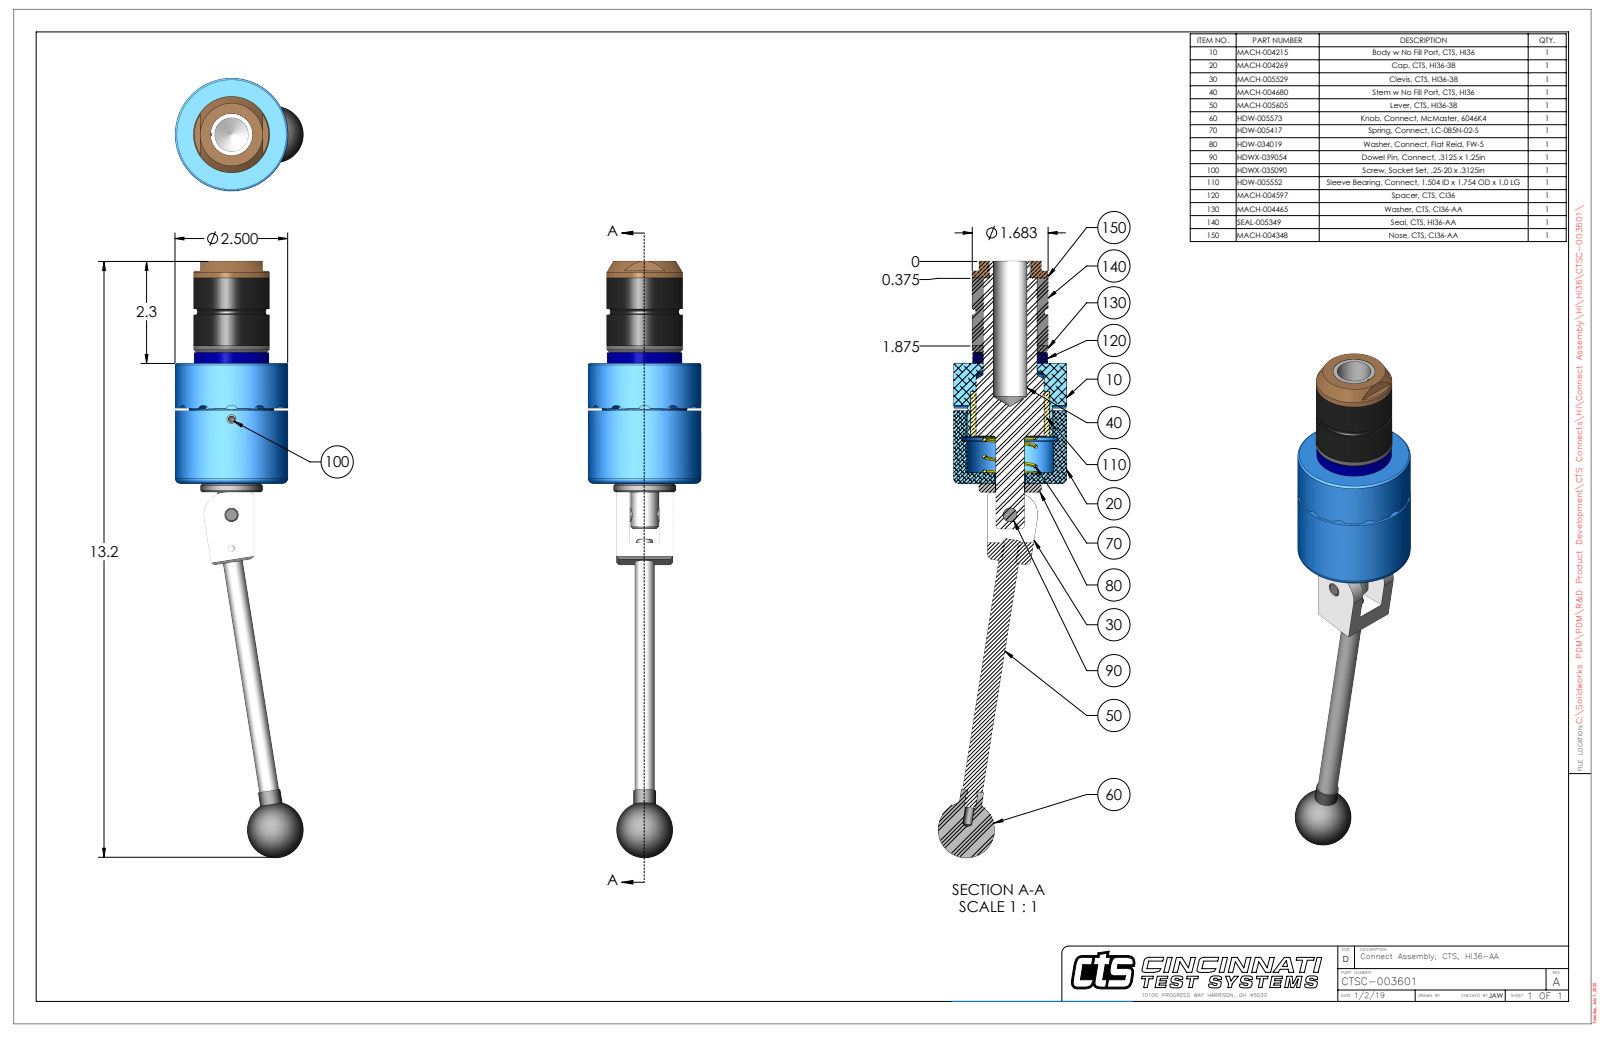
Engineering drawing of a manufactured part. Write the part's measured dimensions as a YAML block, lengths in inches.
part_name: "CTSC-003601"
step_written_by: "SolidWorks 2023 (AUTOMOTIVE_DESIGN)"
units: inches
bodies: {solids: 10, faces: 271, planar: 97, cylindrical: 107, other: 67}
overall_size: [13.215, 2.843, 2.5]
volume: 20
surface_area: 113.2
round_holes:
  - {diameter: 0.201, count: 2}
  - {diameter: 0.15, count: 1}
  - {diameter: 0.311, count: 1}
  - {diameter: 0.313, count: 1}
  - {diameter: 0.314, count: 1}
  - {diameter: 0.656, count: 1}
  - {diameter: 0.696, count: 1}
  - {diameter: 0.75, count: 1}
  - {diameter: 0.922, count: 1}
  - {diameter: 1.188, count: 1}
  - {diameter: 1.19, count: 1}
  - {diameter: 1.198, count: 1}
round_bosses_or_shafts:
  - {diameter: 2.5, count: 1}
  - {diameter: 1.875, count: 1}
  - {diameter: 1.683, count: 1}
  - {diameter: 1.656, count: 1}
  - {diameter: 1.38, count: 1}
  - {diameter: 1.186, count: 1}
  - {diameter: 1, count: 1}
  - {diameter: 0.904, count: 1}
partial_cylinders:
  - {radius: 0.12, count: 12}
  - {radius: 0.029, count: 2}
  - {radius: 0.5, count: 1}
  - {radius: 1.186, count: 1}
face_to_face_distances: [2.668, 4.555, 1.887, 3.055, 0.387, 1.5, 1.62, 1.048, 1.435, 2.935]
hole_center_spacings: [0.74, 2.118, 2.858]
